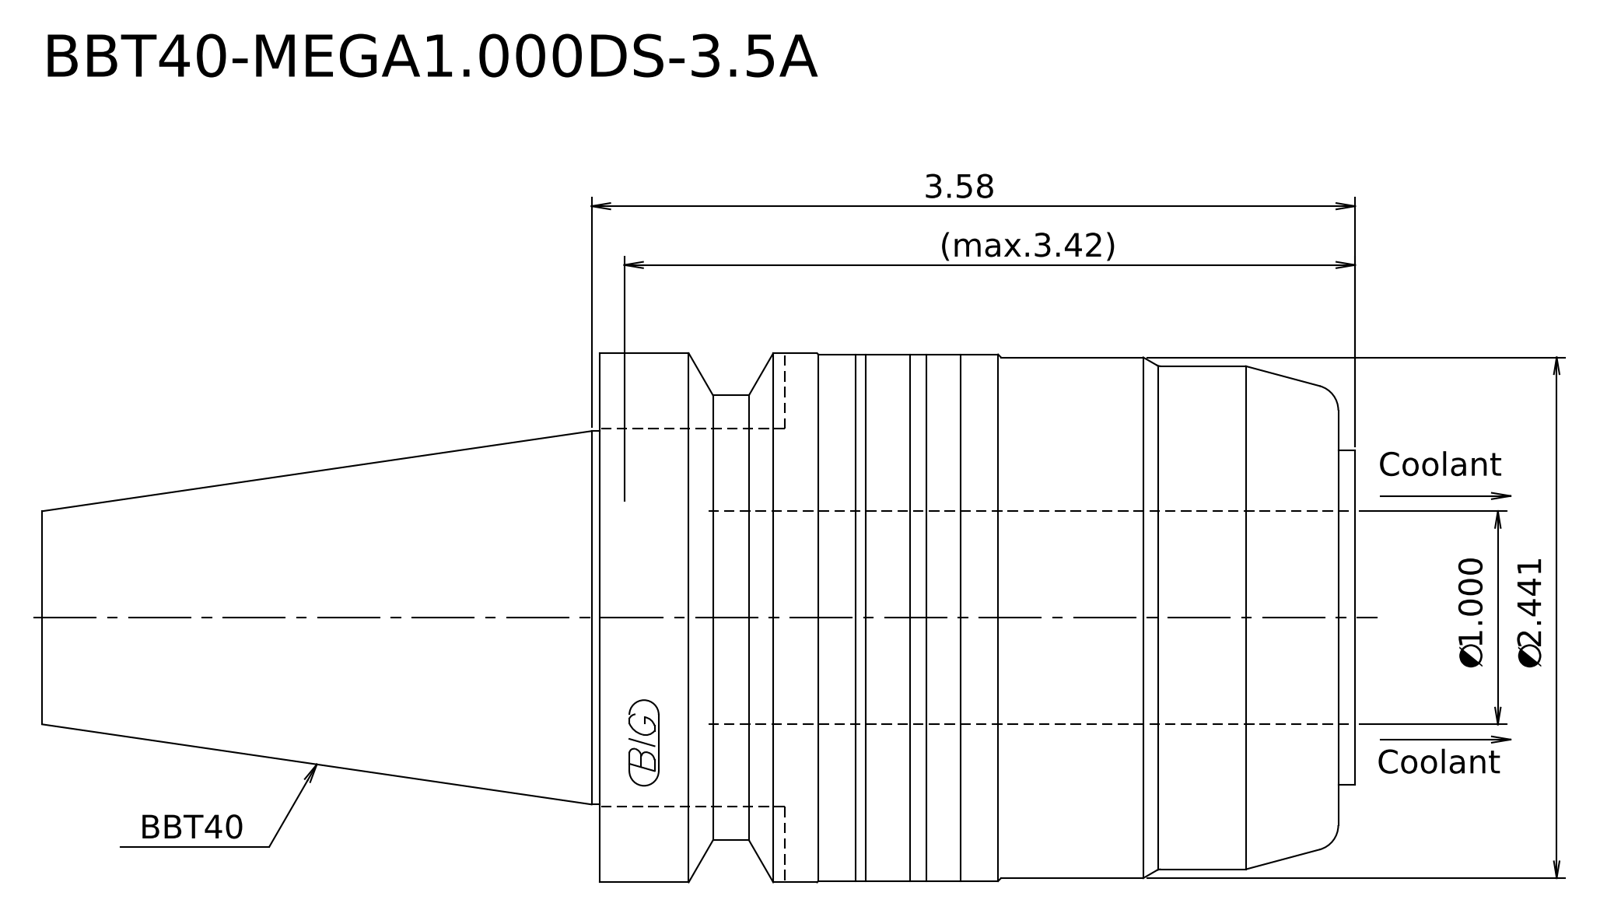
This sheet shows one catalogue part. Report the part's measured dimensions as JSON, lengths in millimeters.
{"step_written_by": "Kubotek KeyCreator 2011 V10.0.2 (22737) (automotive_design)", "units": "millimeters", "bodies": {"solids": 1, "faces": 20, "planar": 4, "cylindrical": 8, "other": 8}, "overall_size": [156.3, 63, 63], "volume_mm3": 323558, "surface_area_mm2": 29988, "round_bosses_or_shafts": [[63, 1], [62.7, 1], [62, 1], [59.9, 1], [53, 1], [44.45, 1], [39.84, 1]], "face_to_face_distances": [89.9, 2, 87.9, 156.3, 154.3, 66.4]}
